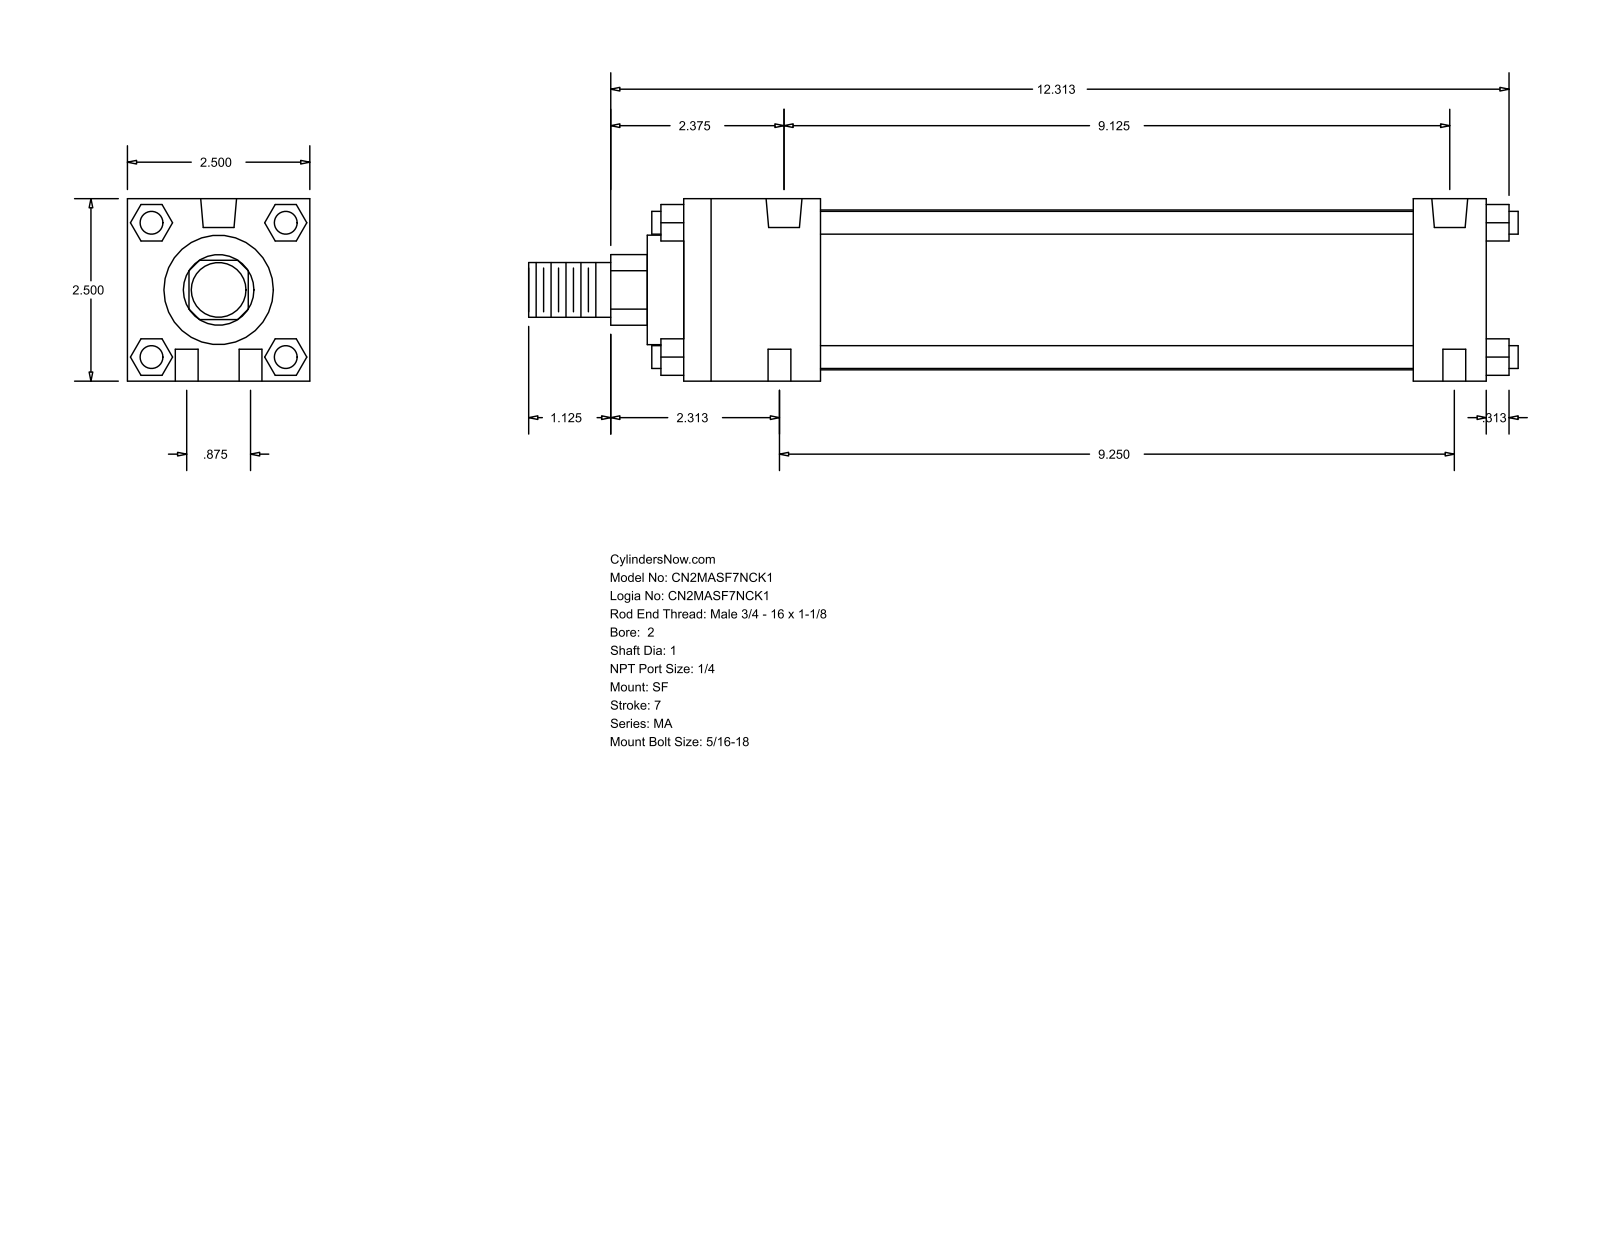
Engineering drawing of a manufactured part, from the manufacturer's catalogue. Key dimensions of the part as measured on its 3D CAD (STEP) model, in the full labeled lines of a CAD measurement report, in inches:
Part name (STEP PRODUCT): MA_SF__0200_1
STEP written by: GSSL Pune (CONFIG_CONTROL_DESIGN)
Units: inches
Bodies: 0 solids, 124 faces (94 planar, 30 cylindrical, 0 other)
Overall size (bounding box): 13.563 × 2.5 × 2.5
Round holes (diameter × count): ⌀0.313 ×6, ⌀0.492 ×2
Round bosses / shafts (diameter × count): ⌀0.313 ×4, ⌀2.19 ×1, ⌀1.5 ×1, ⌀1 ×1, ⌀0.75 ×1
Partial cylindrical surfaces — rounded edges, fillets, slot ends (radius × count): R0.484 ×1
Main face-to-face distances: 2.5, 11, 0.5, 1, 10, 1.875, 8.125, 9.125, 0.92, 1.593
Hole centre spacings: 0.442, 9.198, 0.875, 9.125, 9.25, 9.291
